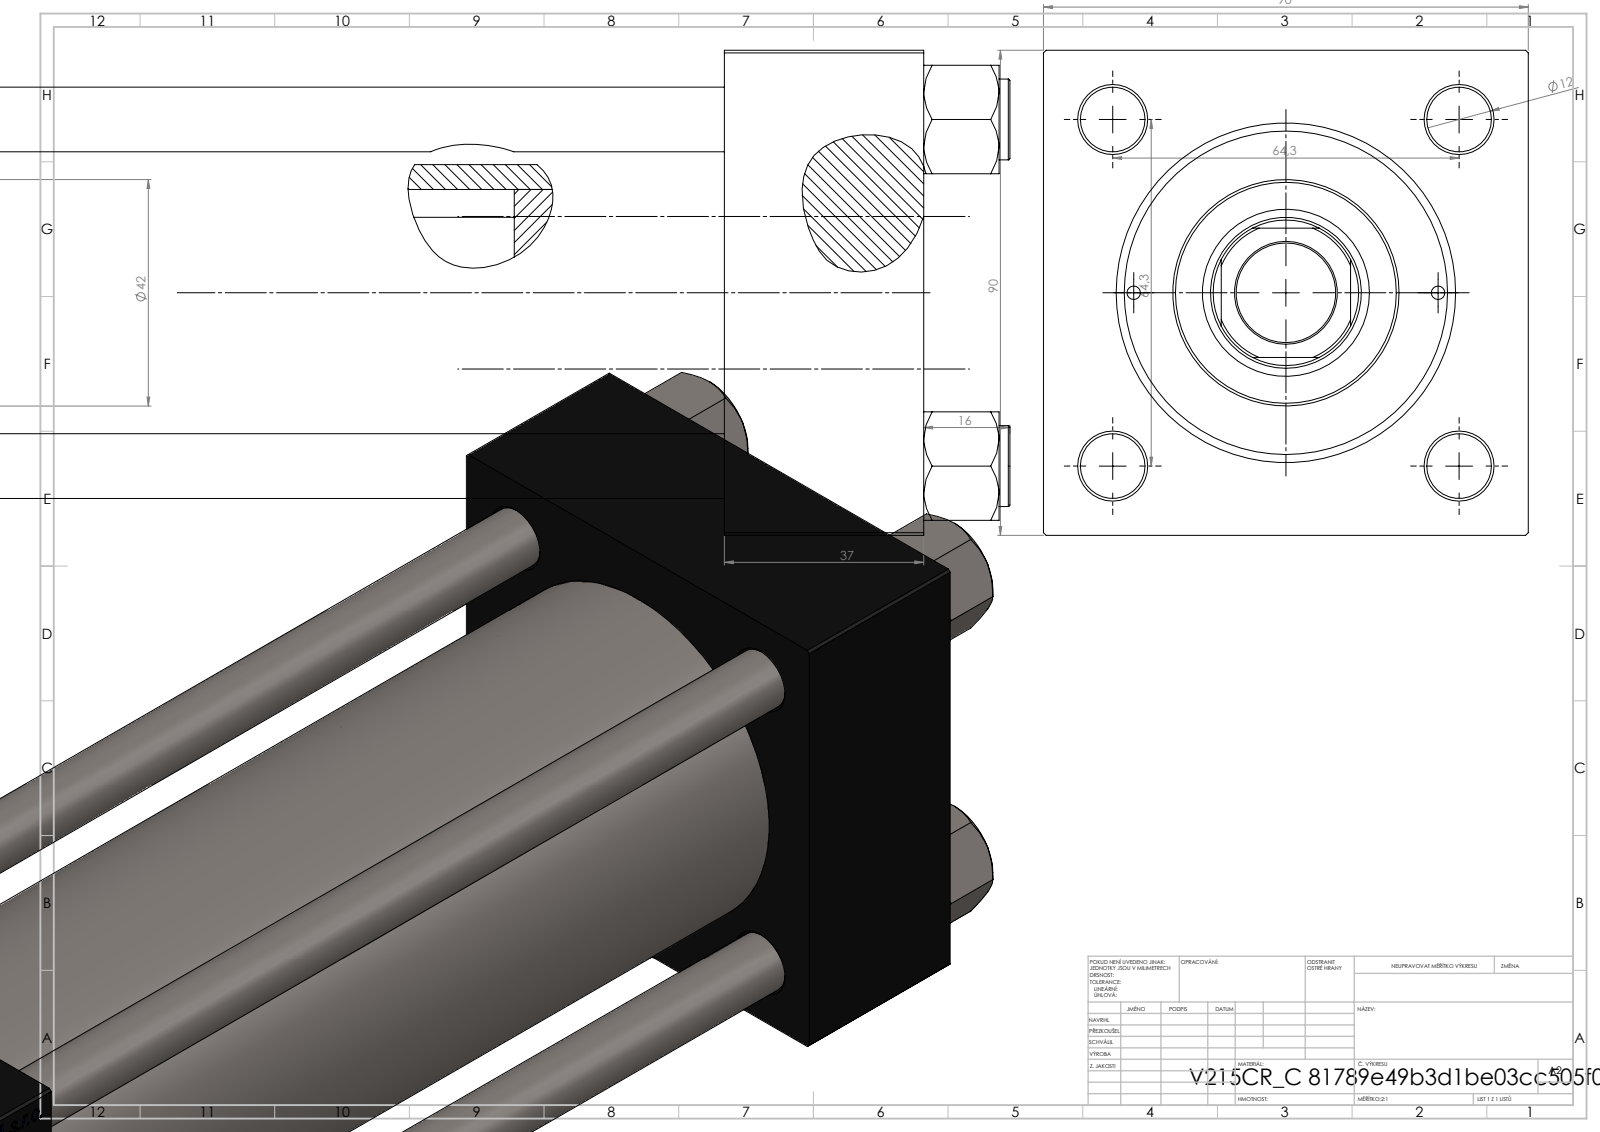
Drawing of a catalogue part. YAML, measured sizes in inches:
part_name: "V215CR_C_TYCINKA; NUT_M5_C; V215_VC_A; V215CR_VCP_C (+1 more)"
step_written_by: "SolidWorks 2019 (CONFIG_CONTROL_DESIGN)"
units: inches
bodies: {solids: 11, faces: 1154, planar: 528, cylindrical: 90, other: 536}
overall_size: [13.504, 3.543, 3.543]
volume: 72.19
surface_area: 419.6
round_holes:
  - {diameter: 0.472, count: 4}
  - {diameter: 0.098, count: 2}
  - {diameter: 0.276, count: 2}
  - {diameter: 0.825, count: 2}
  - {diameter: 1.181, count: 2}
  - {diameter: 0.728, count: 1}
  - {diameter: 1.102, count: 1}
  - {diameter: 1.22, count: 1}
  - {diameter: 1.969, count: 1}
  - {diameter: 2.362, count: 1}
  - {diameter: 2.48, count: 1}
round_bosses_or_shafts:
  - {diameter: 0.591, count: 4}
  - {diameter: 2.717, count: 1}
  - {diameter: 1.654, count: 1}
partial_cylinders:
  - {radius: 0.531, count: 1}
face_to_face_distances: [3.543, 1.457, 11.614, 10.157, 9.291, 7.835, 2.323, 10.484, 9.028, 1.193]
hole_center_spacings: [1.275, 1.79, 2.531, 2.694, 1.112, 3.58, 2.224, 9.35]
